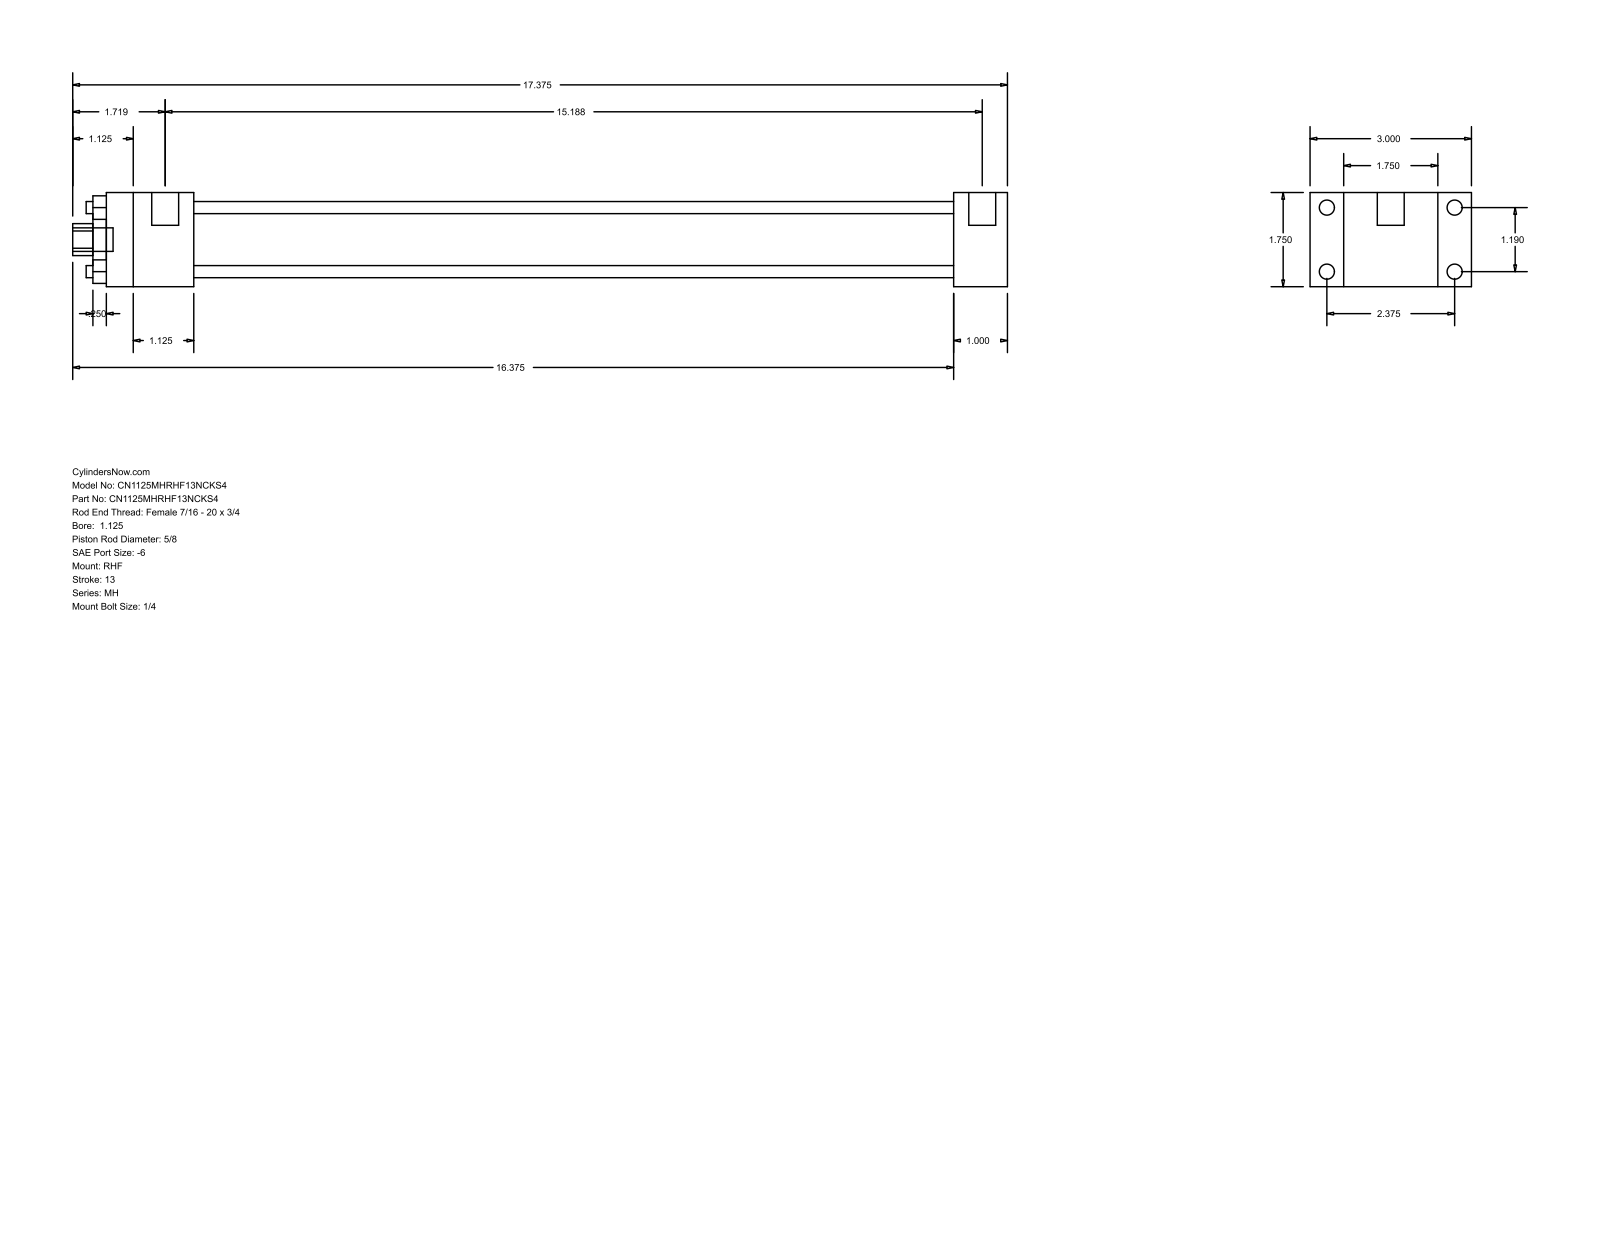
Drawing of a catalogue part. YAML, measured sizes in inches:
part_name: "MH_RHF__0112_0.625"
step_written_by: "GSSL Pune (CONFIG_CONTROL_DESIGN)"
units: inches
bodies: {solids: 0, faces: 88, planar: 60, cylindrical: 28, other: 0}
overall_size: [17.375, 3, 1.75]
round_holes:
  - {diameter: 0.225, count: 4}
  - {diameter: 0.625, count: 1}
  - {diameter: 1.125, count: 1}
  - {diameter: 1.375, count: 1}
round_bosses_or_shafts:
  - {diameter: 0.281, count: 4}
  - {diameter: 0.219, count: 4}
  - {diameter: 0.5, count: 2}
  - {diameter: 0.437, count: 1}
partial_cylinders:
  - {radius: 0.297, count: 1}
face_to_face_distances: [1.75, 0.625, 2.375, 1, 3, 14.125, 15.125, 1.625, 15.75, 16.75]
hole_center_spacings: [0.841, 1.19, 1.683]
